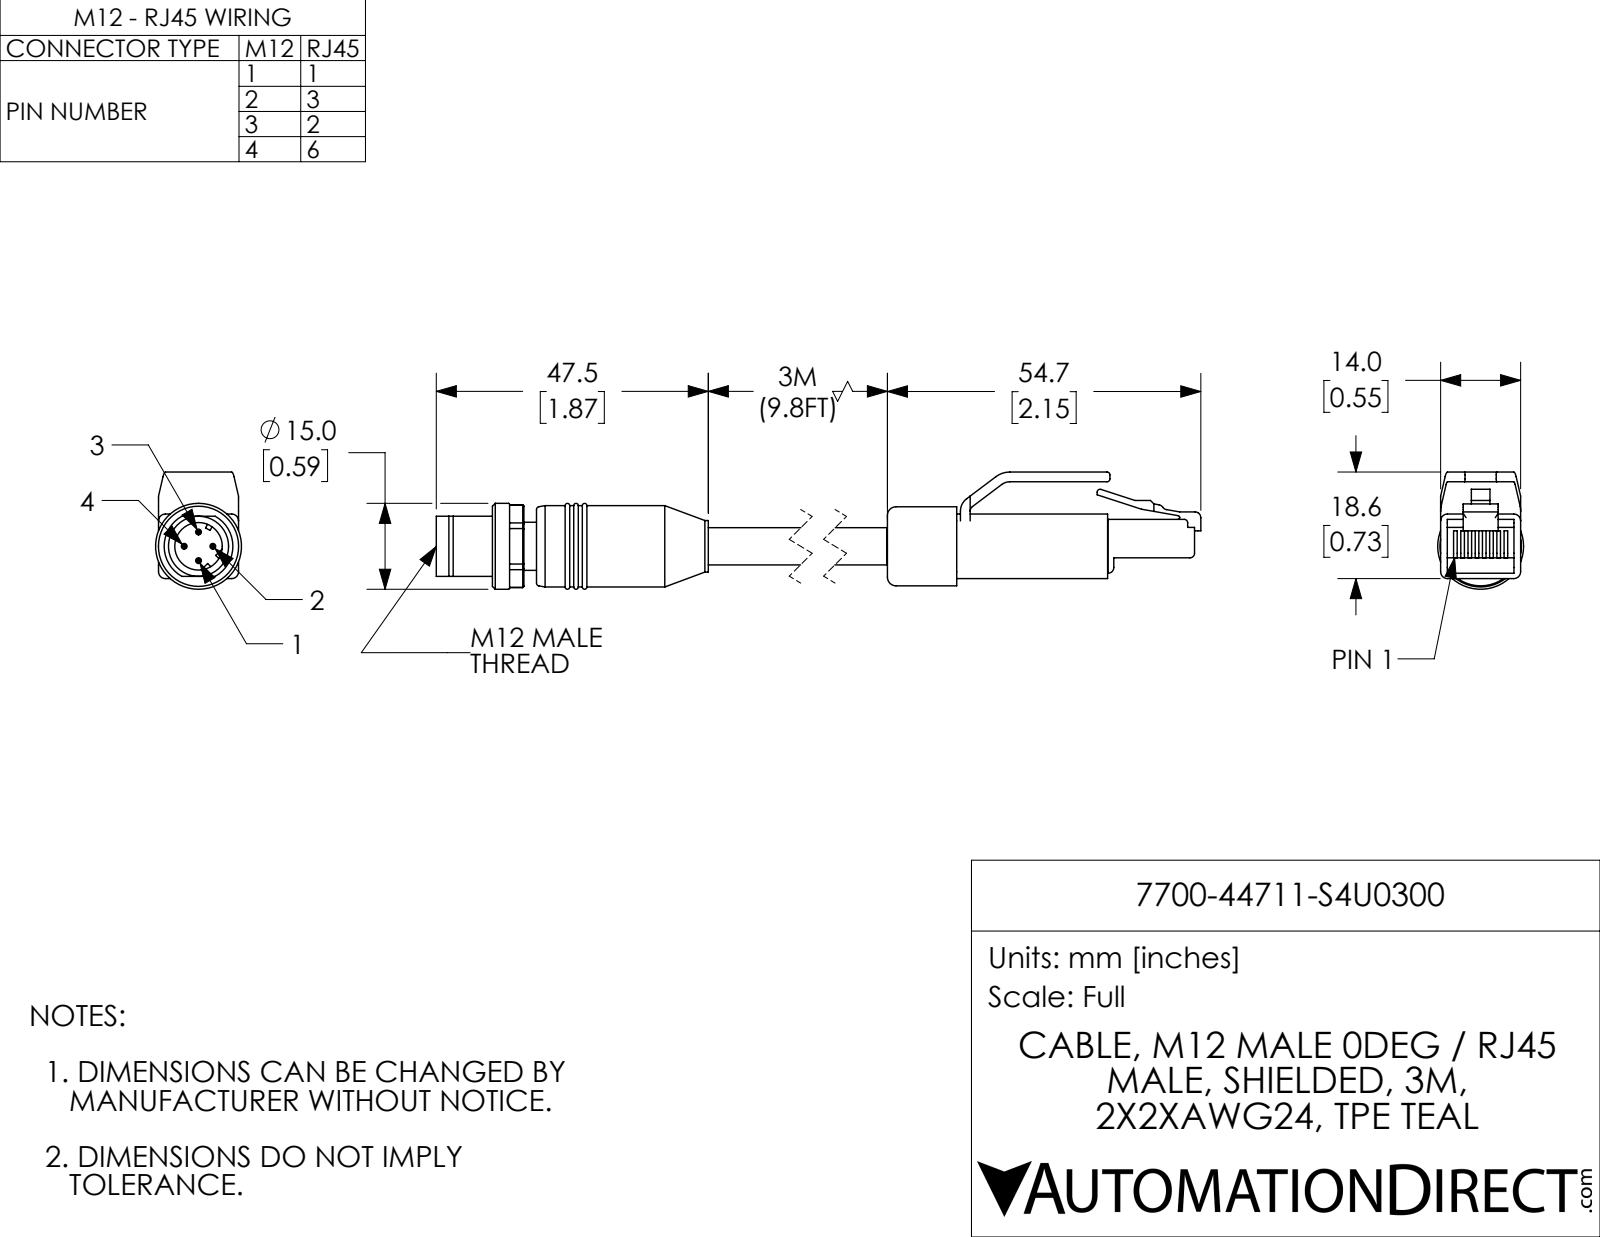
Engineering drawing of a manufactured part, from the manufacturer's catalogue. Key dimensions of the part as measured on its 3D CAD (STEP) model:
Part name (STEP PRODUCT): 7700-44711-S4U0300_MALE; 7700-44711-S4U0300; 7700-44711-S4U0300_RJ45
STEP written by: SolidWorks 2017 (AUTOMOTIVE_DESIGN)
Units: inches
Bodies: 4 solids, 230 faces (121 planar, 67 cylindrical, 42 other)
Overall size (bounding box): 5.761 × 0.806 × 0.591
Volume: 0.896 in³ · Surface area: 11.27 in²
Round holes (diameter × count): ⌀0.327 ×1
Round bosses / shafts (diameter × count): ⌀0.039 ×4, ⌀0.591 ×1, ⌀0.559 ×1, ⌀0.543 ×1, ⌀0.413 ×1, ⌀0.354 ×1, ⌀0.331 ×1, ⌀0.256 ×1
Partial cylindrical surfaces — rounded edges, fillets, slot ends (radius × count): R0.047 ×6, R0.02 ×5, R0.039 ×5, R0.012 ×2, R0.024 ×1, R0.031 ×1, R0.091 ×1, R0.106 ×1
Main face-to-face distances: 0.444, 0.55, 0.067, 0.143, 0.301, 0.407, 0.264, 0.037, 0.665, 0.732
